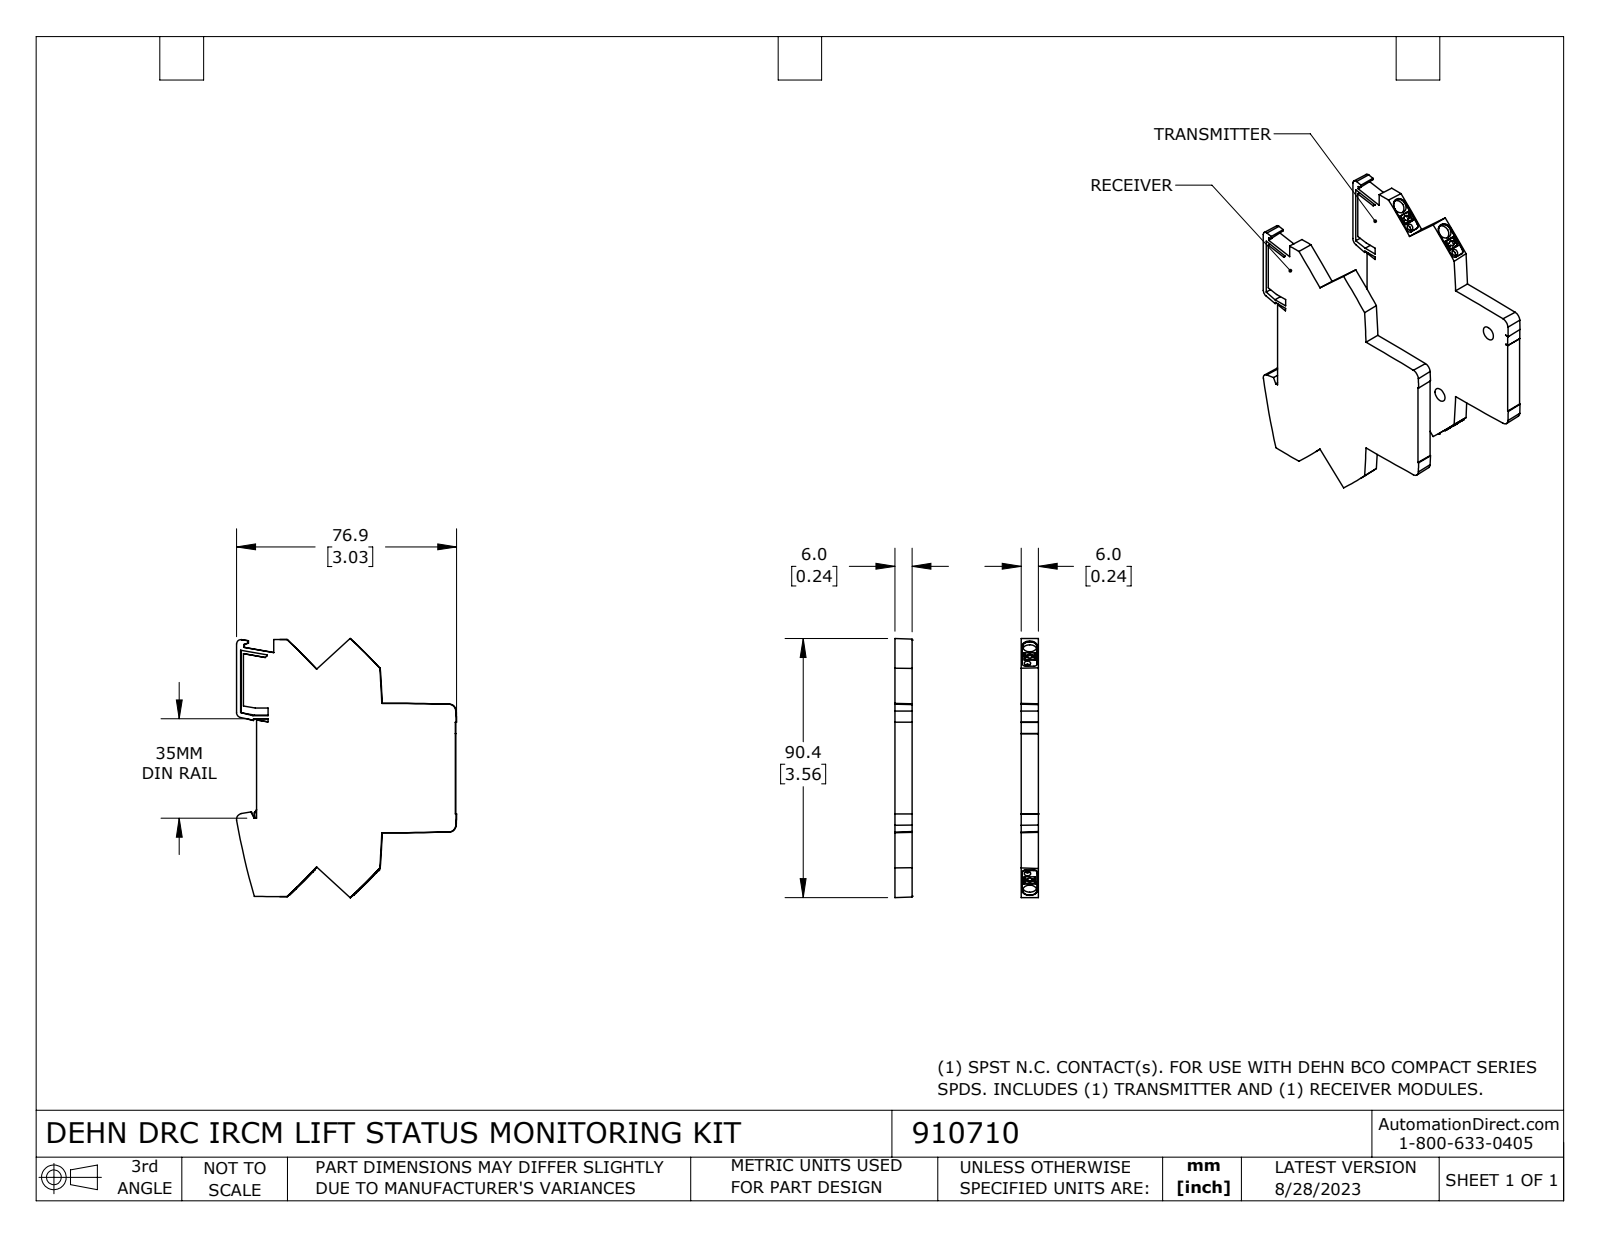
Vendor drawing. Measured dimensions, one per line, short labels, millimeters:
name: 910710; 910710_TRANSMITTER; 910710_RECEIVER
written by: SolidWorks 2021 (CONFIG_CONTROL_DESIGN)
unit: mm
bodies: 2 solids, 324 faces (197 planar, 30 cylindrical, 97 other)
size: 90.4 × 76.9 × 50.1
volume: 58 830 mm³; area: 25 830 mm²
holes: 5× ⌀5
rounds: 3× R0.1, 2× R249.8, 2× R250, 2× R250.2, 1× R1.8, 1× R2, 1× R249.7, 1× R250.3
face distances: 44.1, 6, 50.1, 38.1, 0.6, 75, 1, 74.4, 75.5, 0.4
hole spacings: 15.5
